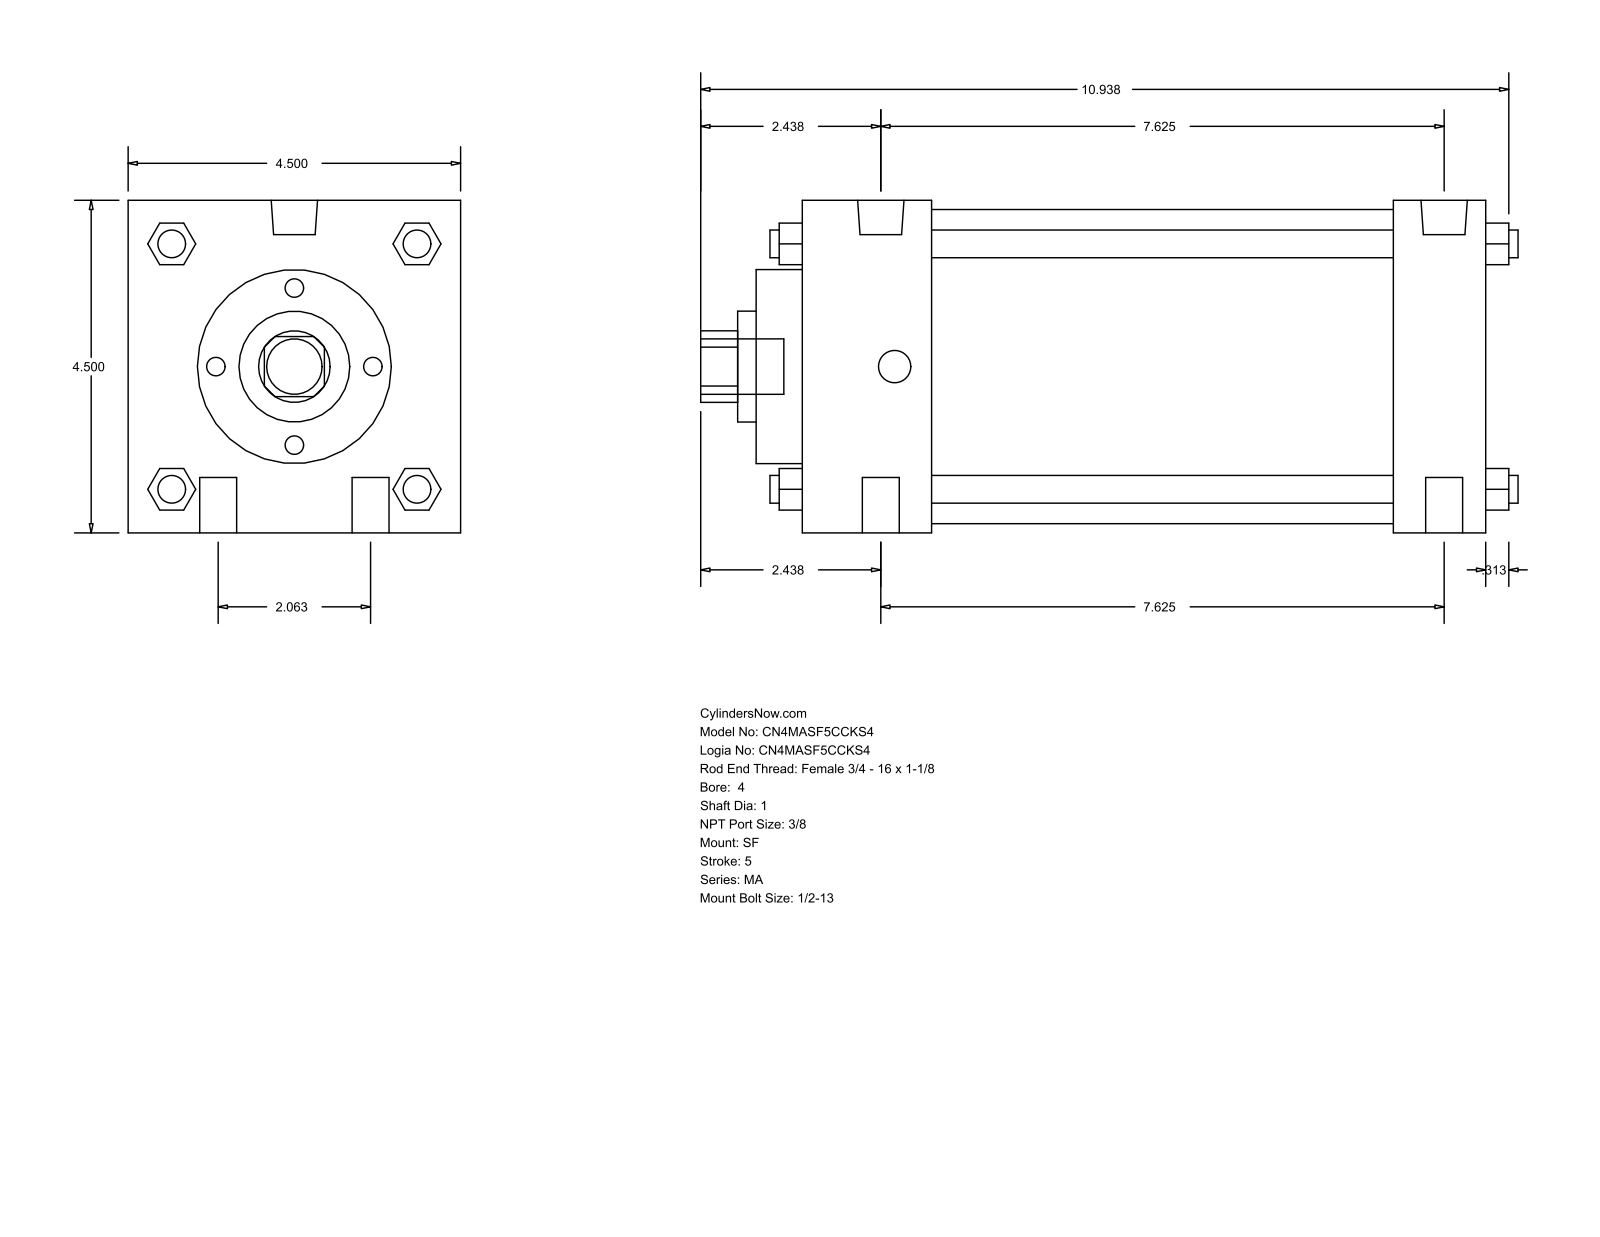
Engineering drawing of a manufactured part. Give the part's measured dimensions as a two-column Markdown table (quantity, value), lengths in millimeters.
| quantity | value |
| --- | --- |
| part name | MA_SF__0400_1 |
| STEP written by | GSSL Pune (CONFIG_CONTROL_DESIGN) |
| units | millimeters |
| bodies | 0 solids, 126 faces (95 planar, 31 cylindrical, 0 other) |
| overall size | 280.99 × 114.3 × 114.3 |
| round holes (diameter × count) | 25.4 × 1, 38.1 × 1, 66.67 × 1, 107.95 × 1 |
| round bosses / shafts (diameter × count) | 12.7 × 4, 9.53 × 4, 15.93 × 2, 11.11 × 2, 19.05 × 1 |
| partial cylindrical surfaces (radius × count) | 12.29 × 1 |
| main face-to-face distances | 114.3, 234.96, 203.2, 31.76, 44.46, 158.74, 190.5, 15.87, 60.33, 219.07 |
